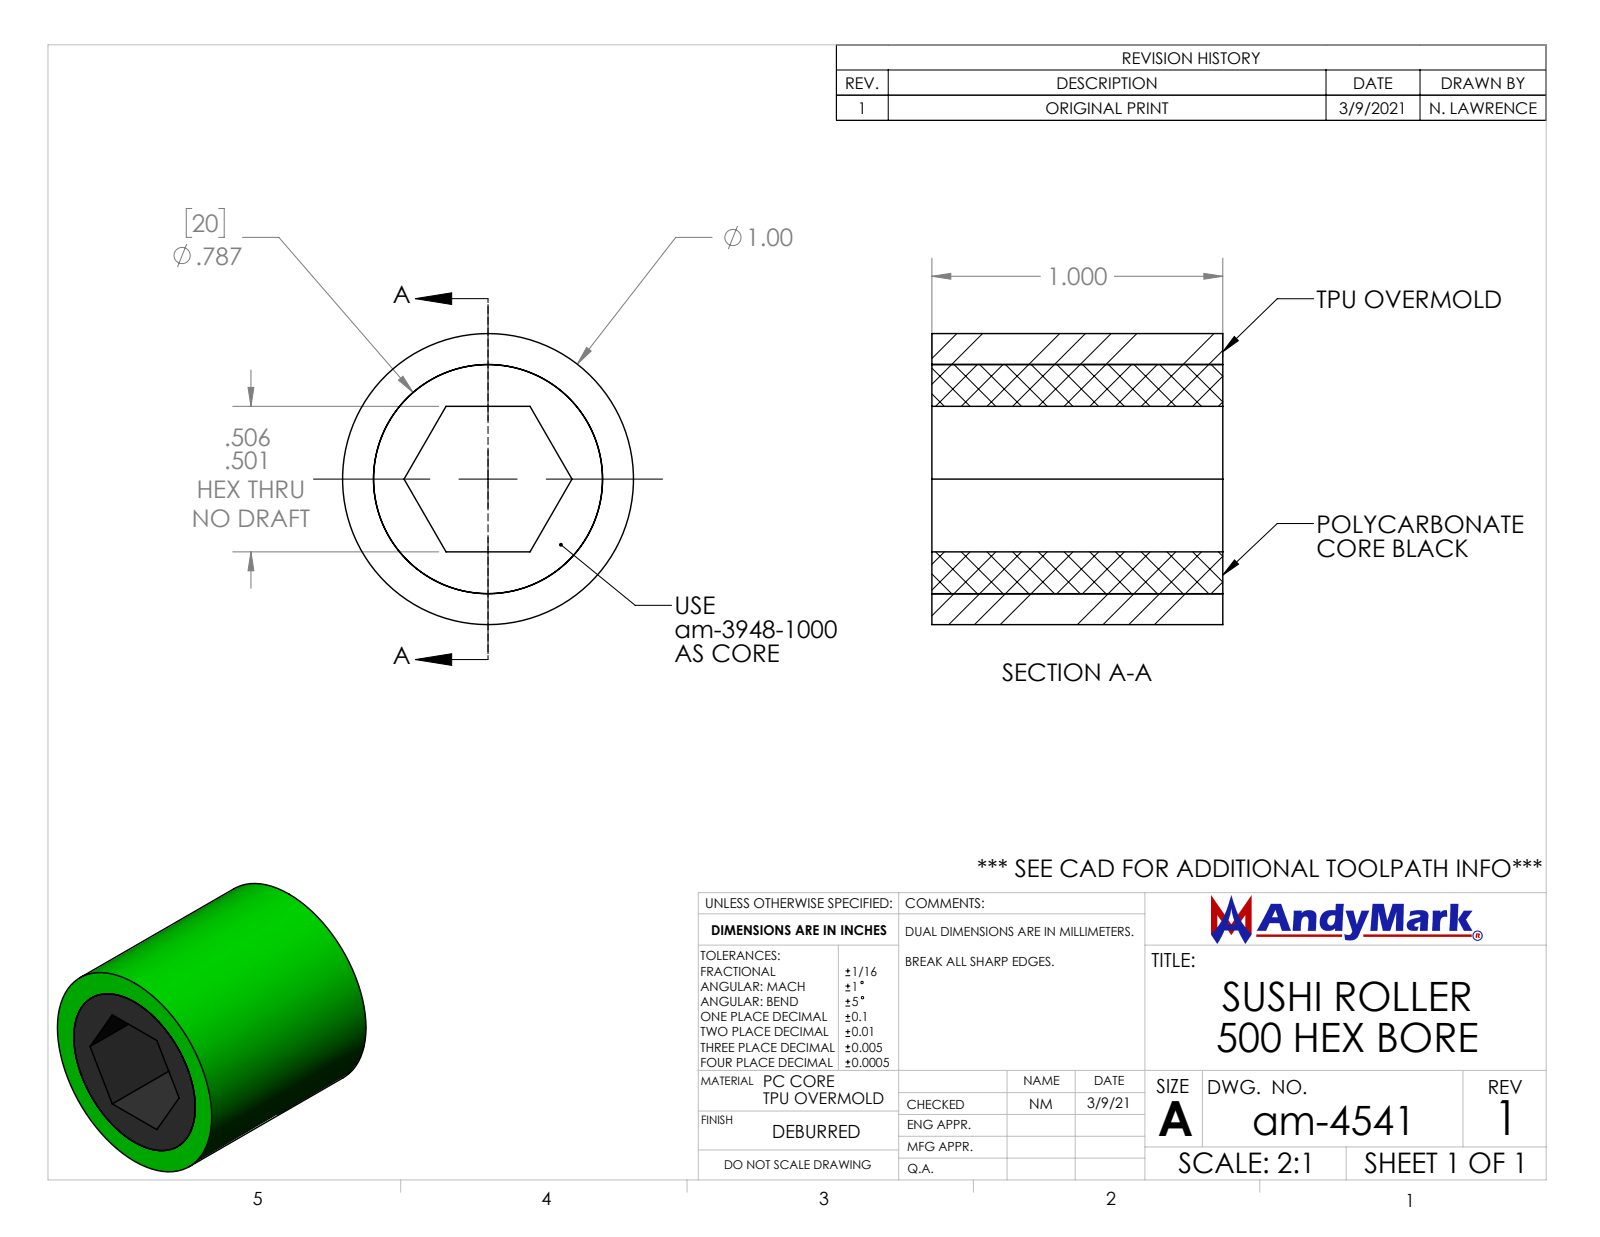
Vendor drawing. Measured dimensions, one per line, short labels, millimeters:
name: am-4541 Sushi Roller 500 Hex Bore
written by: SolidWorks 2019 (AUTOMOTIVE_DESIGN)
unit: mm
bodies: 2 solids, 13 faces (10 planar, 3 cylindrical, 0 other)
size: 25.4 × 25.4 × 25.4
volume: 9 322 mm³; area: 7 070 mm²
holes: 1× ⌀20
bosses: 1× ⌀25.4
face distances: 12.7, 25.4
